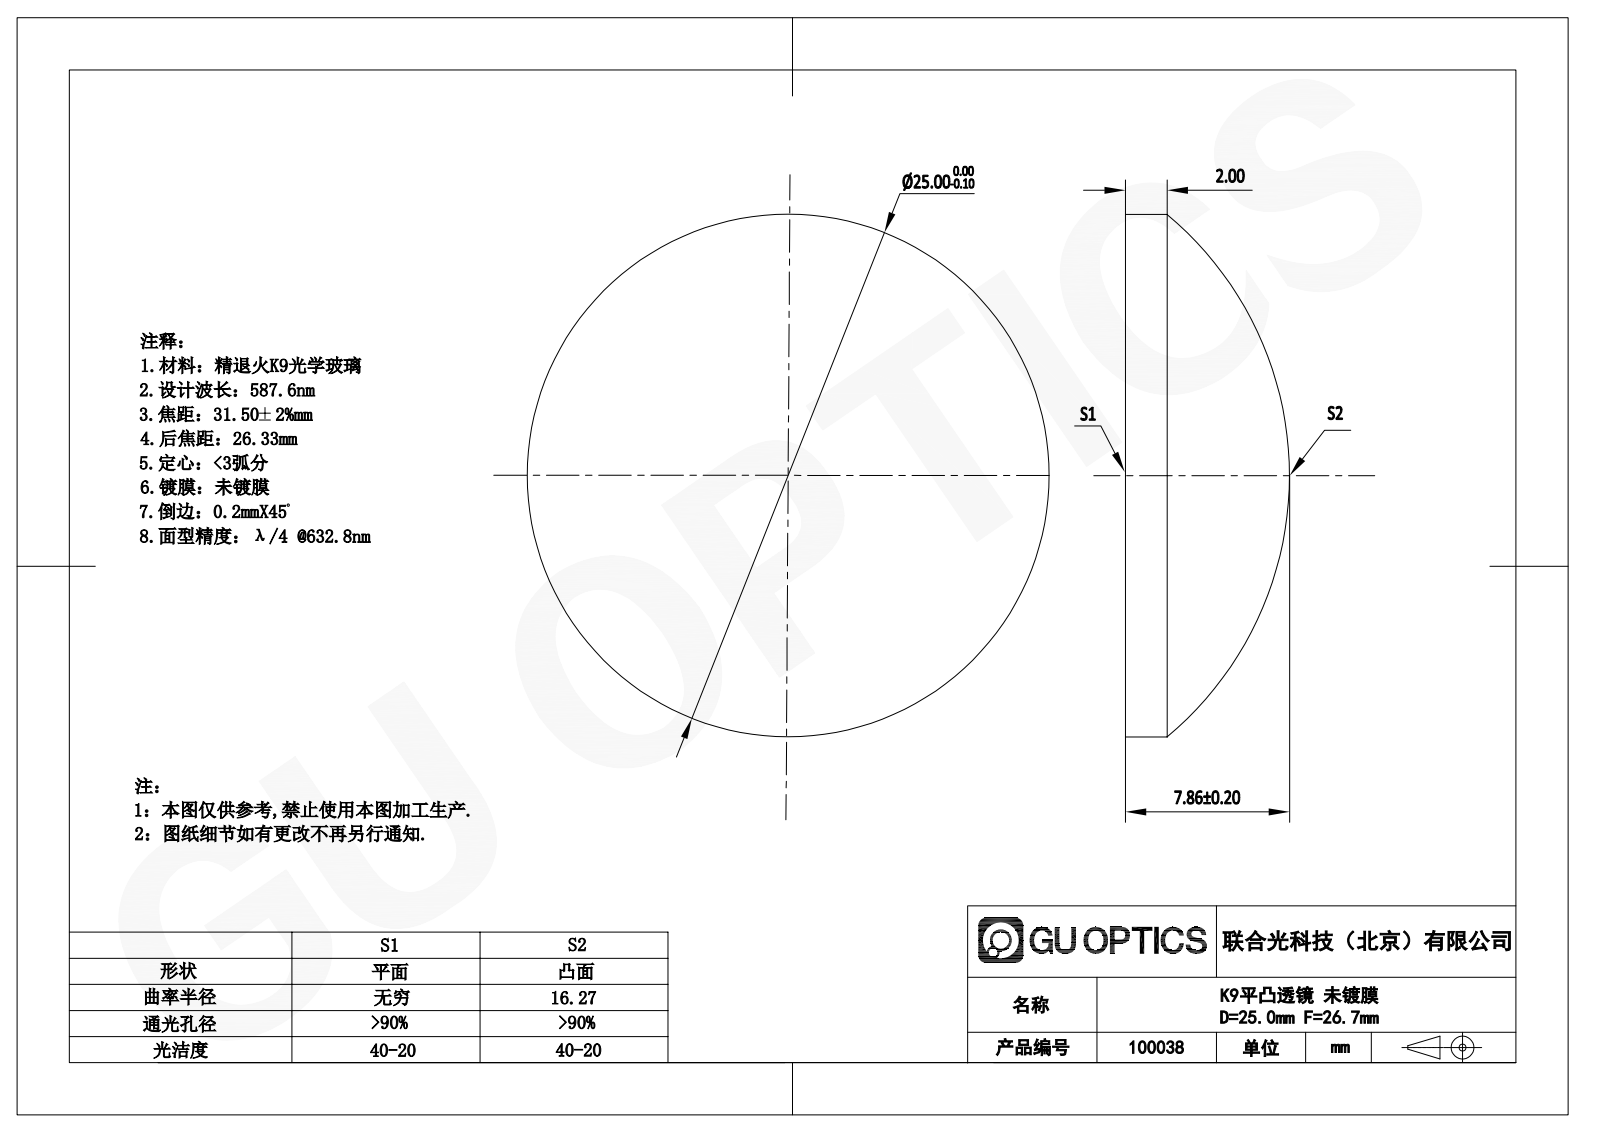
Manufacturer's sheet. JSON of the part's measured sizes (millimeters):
{"part_name": "100038", "step_written_by": "SolidWorks 2016 (AUTOMOTIVE_DESIGN)", "units": "millimeters", "bodies": {"solids": 1, "faces": 5, "planar": 1, "cylindrical": 2, "other": 2}, "overall_size": [25, 25, 7.86], "volume_mm3": 2525, "surface_area_mm2": 1247, "round_bosses_or_shafts": [[25, 1]]}
